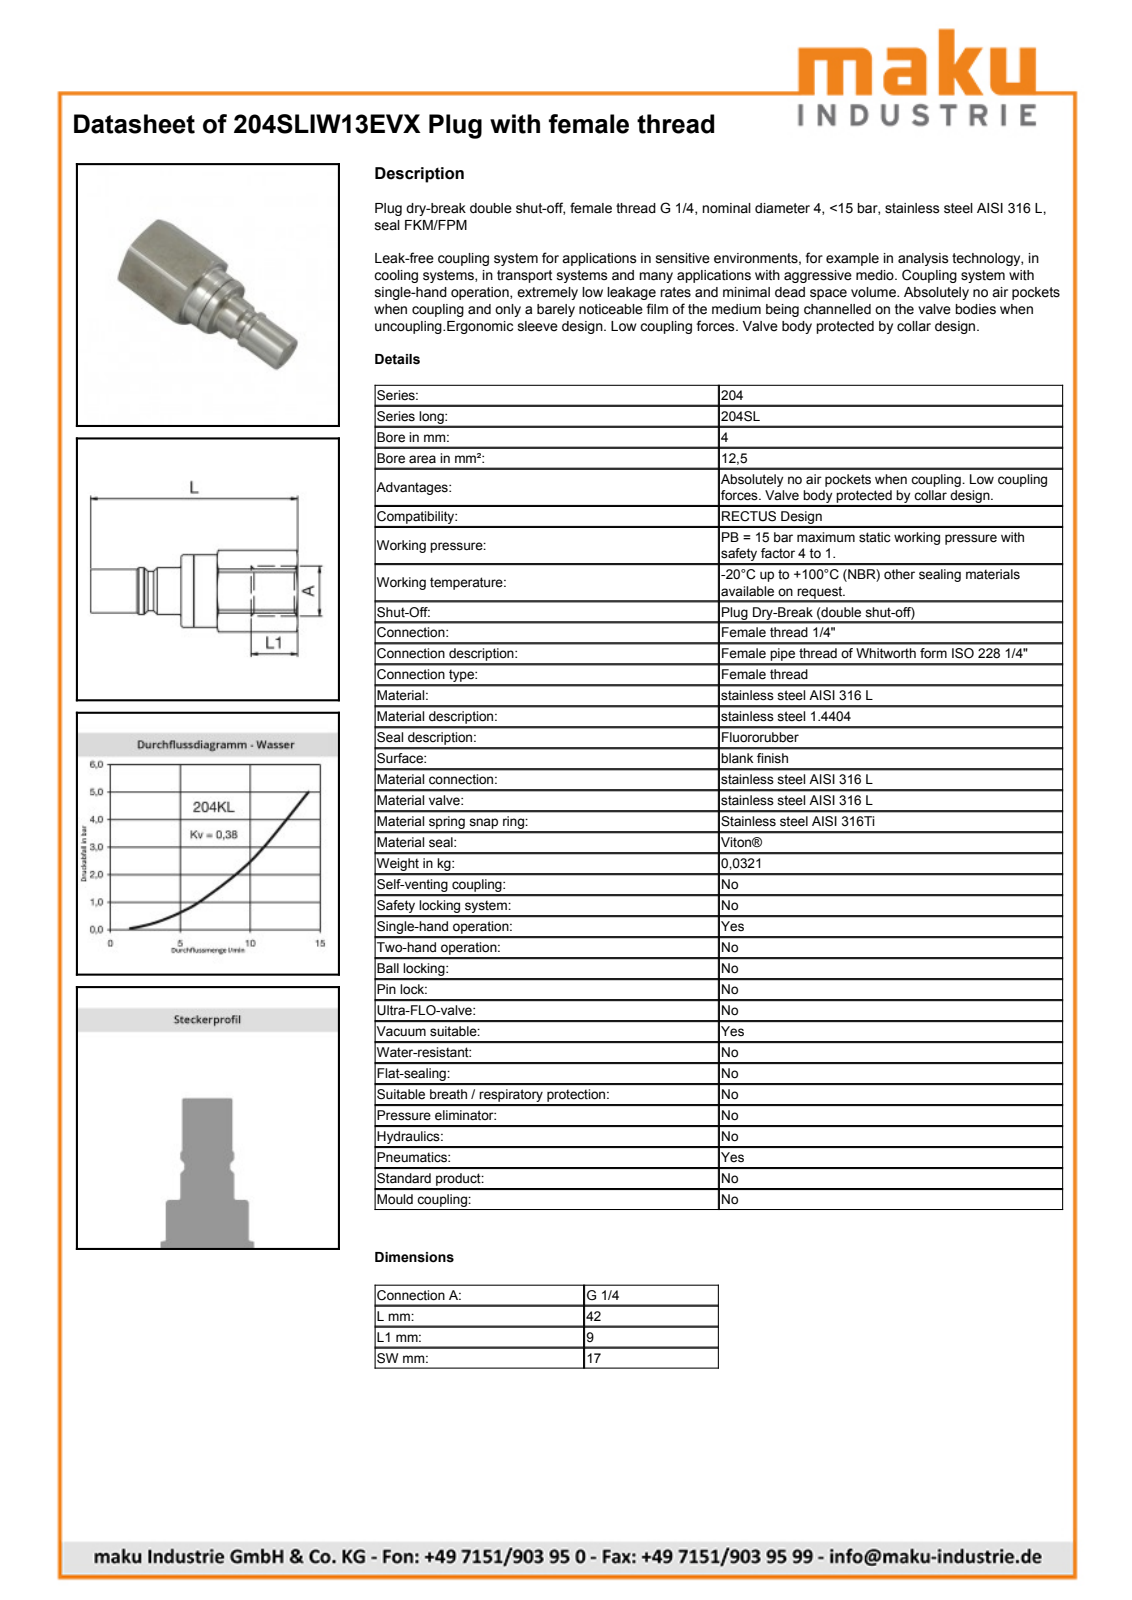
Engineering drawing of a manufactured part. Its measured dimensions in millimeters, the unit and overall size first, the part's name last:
Units: millimetres
Overall size (bounding box): 41.9 × 19.15 × 17.2
Round holes (diameter × count): ⌀7.6 ×1, ⌀11.45 ×1
Round bosses / shafts (diameter × count): ⌀14 ×1, ⌀12.2 ×1, ⌀9 ×1, ⌀8.4 ×1, ⌀6.8 ×1
Partial cylindrical surfaces — rounded edges, fillets, slot ends (radius × count): R9.57 ×1
Main face-to-face distances: 17, 9, 8.55, 17.55, 6.85, 15.4, 24.4, 17.5, 24.35, 32.9
Volume: 5 481 mm³ · Surface area: 2 690 mm²
Bodies: 1 solid, 57 faces (14 planar, 16 cylindrical, 27 other)
Part name (STEP PRODUCT): D110034
STEP written by: Autodesk Inventor 2013 (AUTOMOTIVE_DESIGN)
